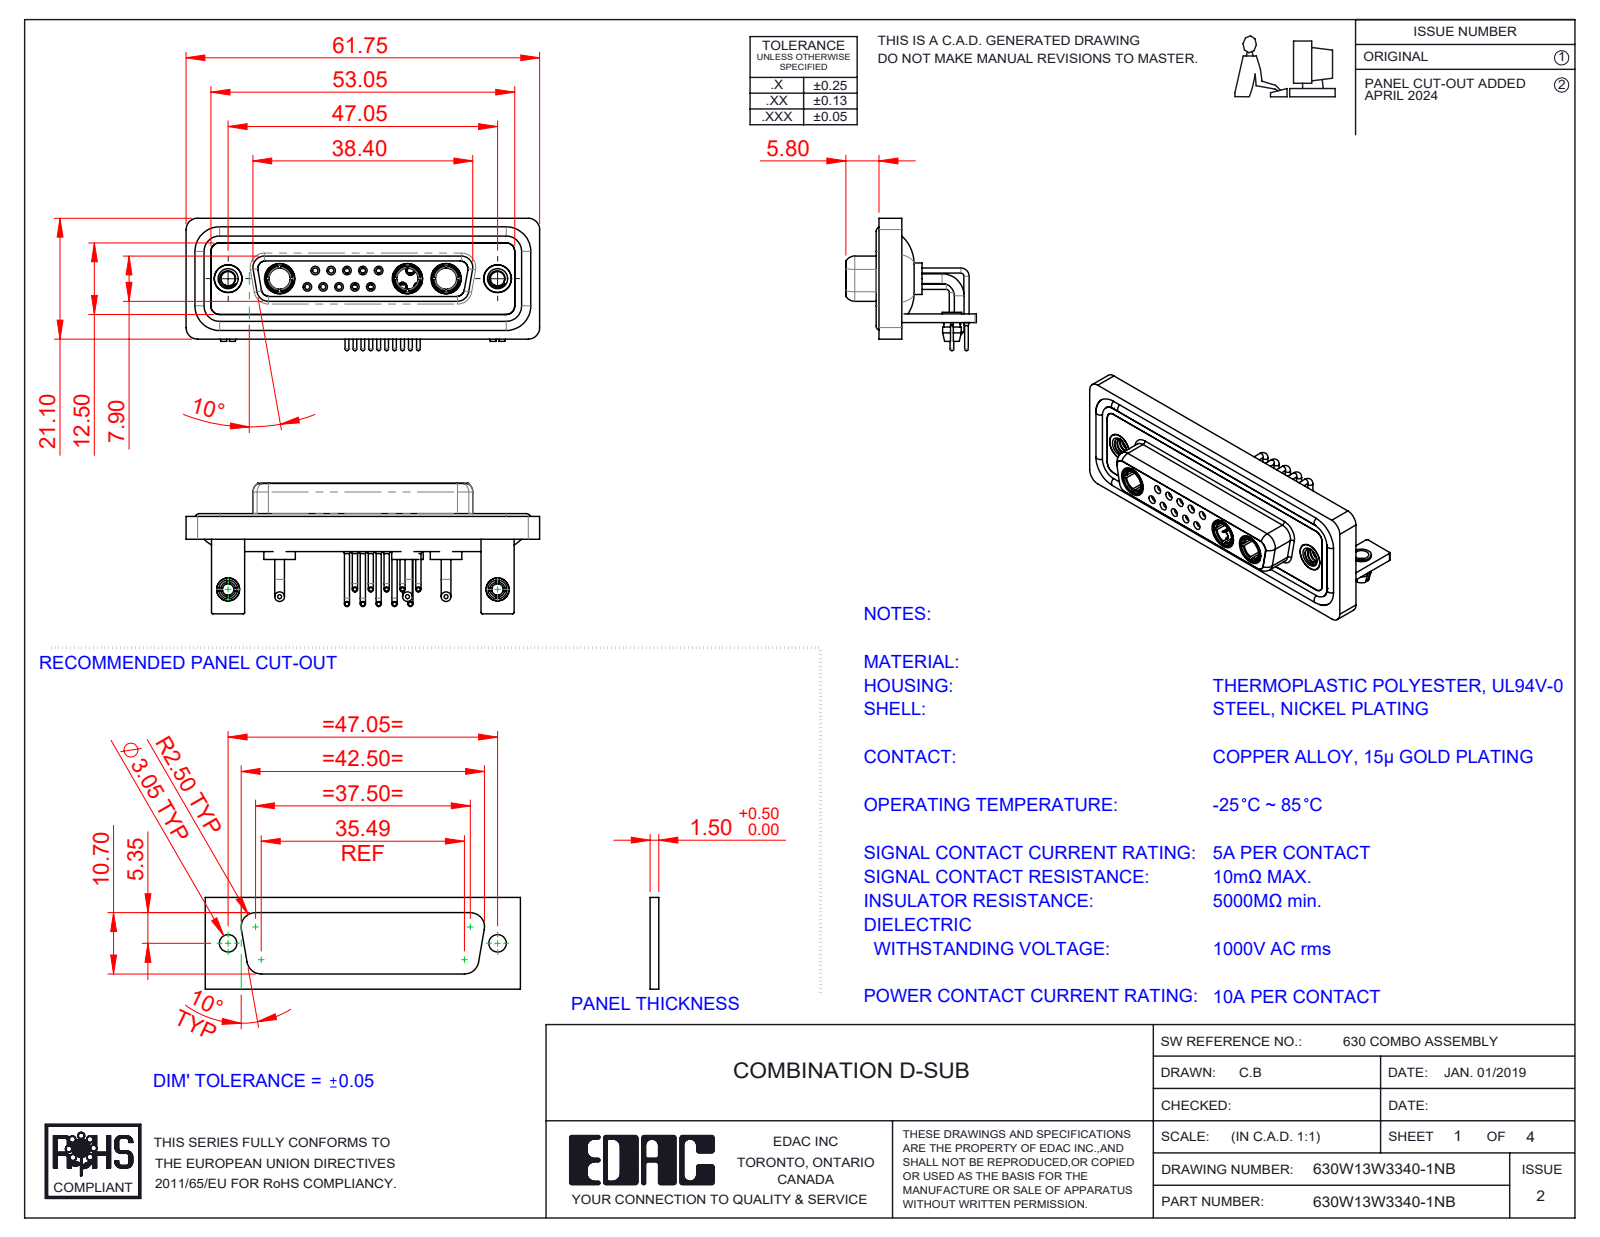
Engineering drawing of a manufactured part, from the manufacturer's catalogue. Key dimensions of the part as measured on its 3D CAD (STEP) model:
Part name (STEP PRODUCT): 630Combo Housing_13W3; 630Combo Shell Front_25 Contacts; 630Combo Threaded Rivet_A; 630W13W3340-1NB (+7 more)
STEP written by: SolidWorks 2023 (CONFIG_CONTROL_DESIGN)
Units: millimetres
Bodies: 27 solids, 1284 faces (410 planar, 547 cylindrical, 327 other)
Overall size (bounding box): 61.75 × 23.12 × 22.8
Volume: 8 693 mm³ · Surface area: 15 093 mm²
Round holes (diameter × count): ⌀2 ×12, ⌀0.9 ×10, ⌀1.1 ×10, ⌀1.5 ×10, ⌀1.6 ×5, ⌀1.7 ×5, ⌀4.85 ×5, ⌀2.5 ×4, ⌀3.7 ×3, ⌀5.3 ×3, ⌀3.2 ×2, ⌀4 ×2
Round bosses / shafts (diameter × count): ⌀0.9 ×15, ⌀1.6 ×12, ⌀0.65 ×10, ⌀1.7 ×6, ⌀2 ×5, ⌀1.5 ×5, ⌀5.5 ×3, ⌀5.2 ×3
Partial cylindrical surfaces — rounded edges, fillets, slot ends (radius × count): R2 ×19, R1.5 ×18, R0.25 ×16, R1.35 ×8, R1.6 ×8, R0.5 ×5, R0.6 ×4, R0.65 ×4
Main face-to-face distances: 0.4, 1.8, 2.9, 1.5, 3.7, 4.1, 1.1, 1.4, 1.6, 3.1
Hole centre spacings: 3.16, 2.77, 5.54, 5.04, 8.31, 5.03, 7.49, 11.08
